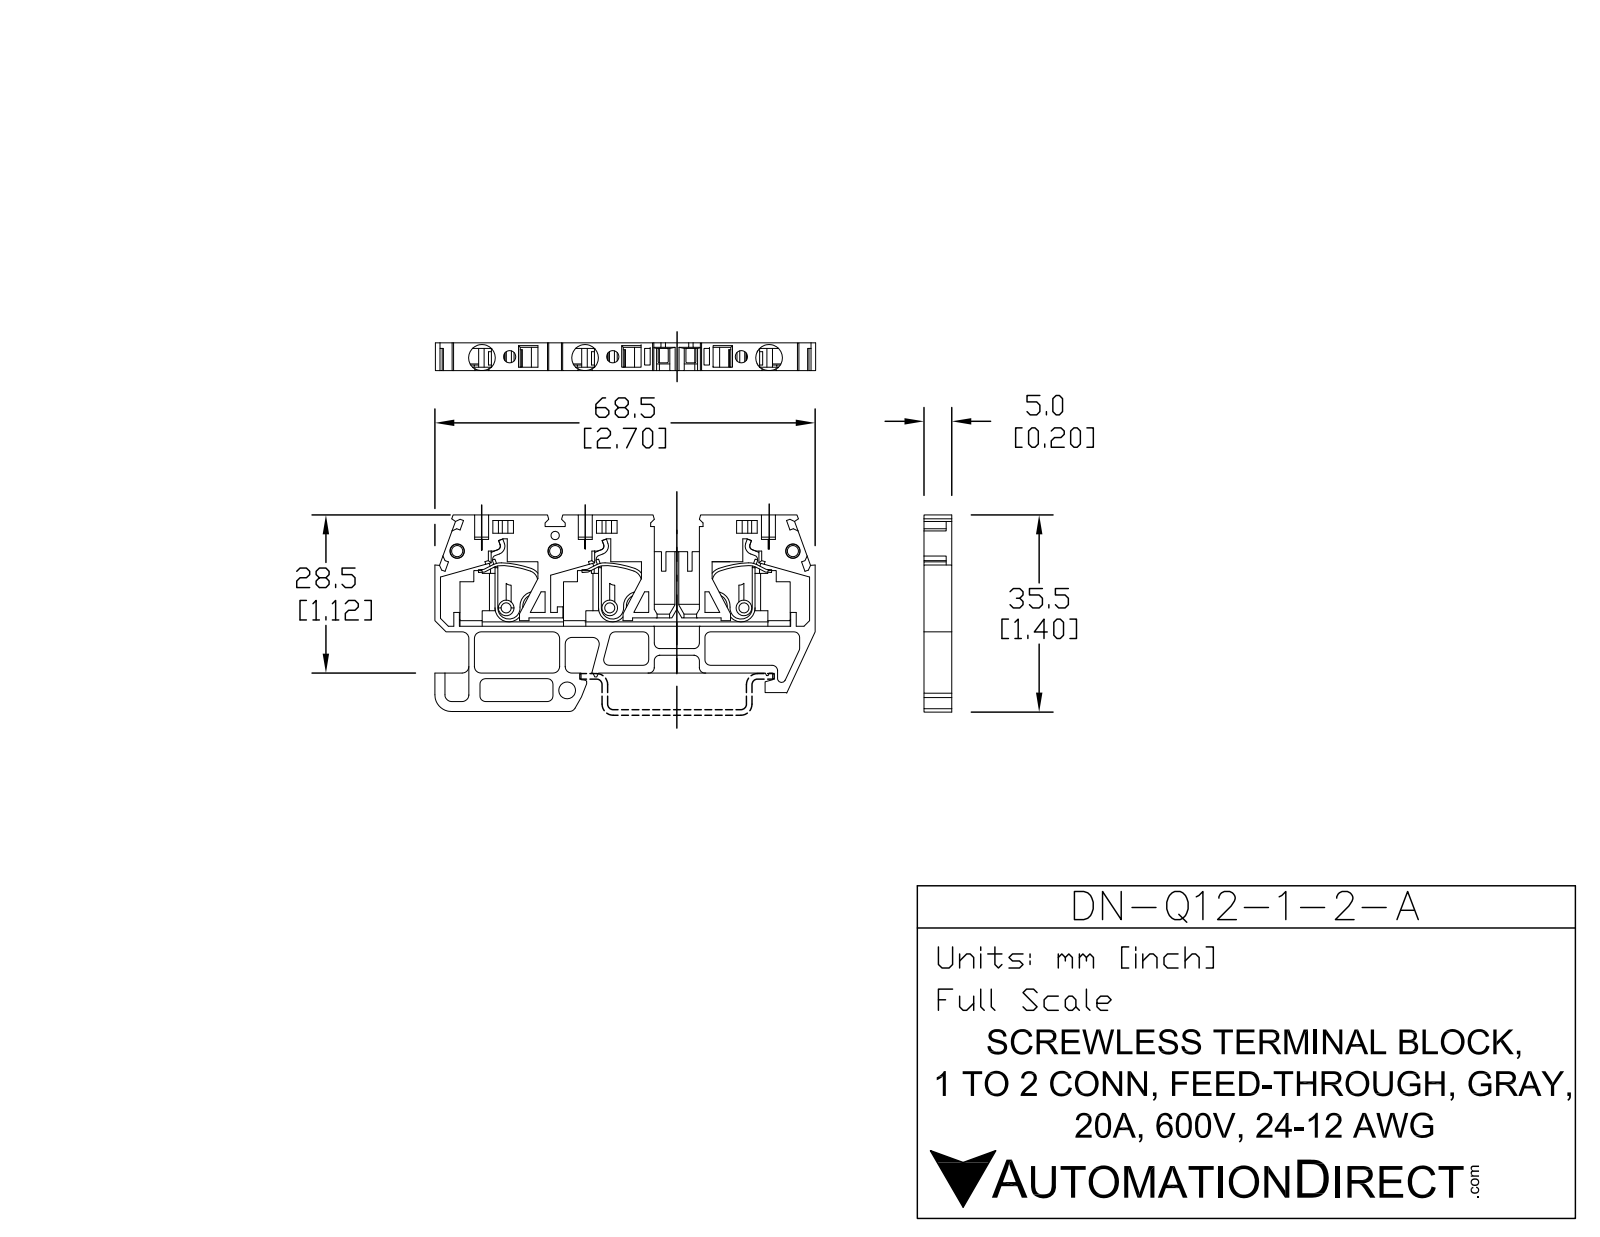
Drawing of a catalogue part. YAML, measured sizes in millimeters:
part_name: "42413_DN-Q12-1-2-A"
step_written_by: "SolidWorks 2013 (AUTOMOTIVE_DESIGN)"
units: millimeters
bodies: {solids: 1, faces: 373, planar: 273, cylindrical: 70, other: 30}
overall_size: [68.6, 35.4, 5]
volume: 6668
surface_area: 6965
round_holes:
  - {diameter: 2.2, count: 3}
  - {diameter: 2.6, count: 3}
  - {diameter: 4.8, count: 3}
  - {diameter: 1.5, count: 1}
  - {diameter: 3, count: 1}
partial_cylinders:
  - {radius: 1, count: 17}
  - {radius: 1.2, count: 12}
  - {radius: 0.3, count: 1}
  - {radius: 0.7, count: 1}
  - {radius: 3, count: 1}
face_to_face_distances: [5, 1, 2, 4.9, 3, 8.4, 7.5, 2.9, 1.9, 28.5]
hole_center_spacings: [5, 18.6, 28.2, 46.8, 2.8, 13.6, 17.6, 17.82]
